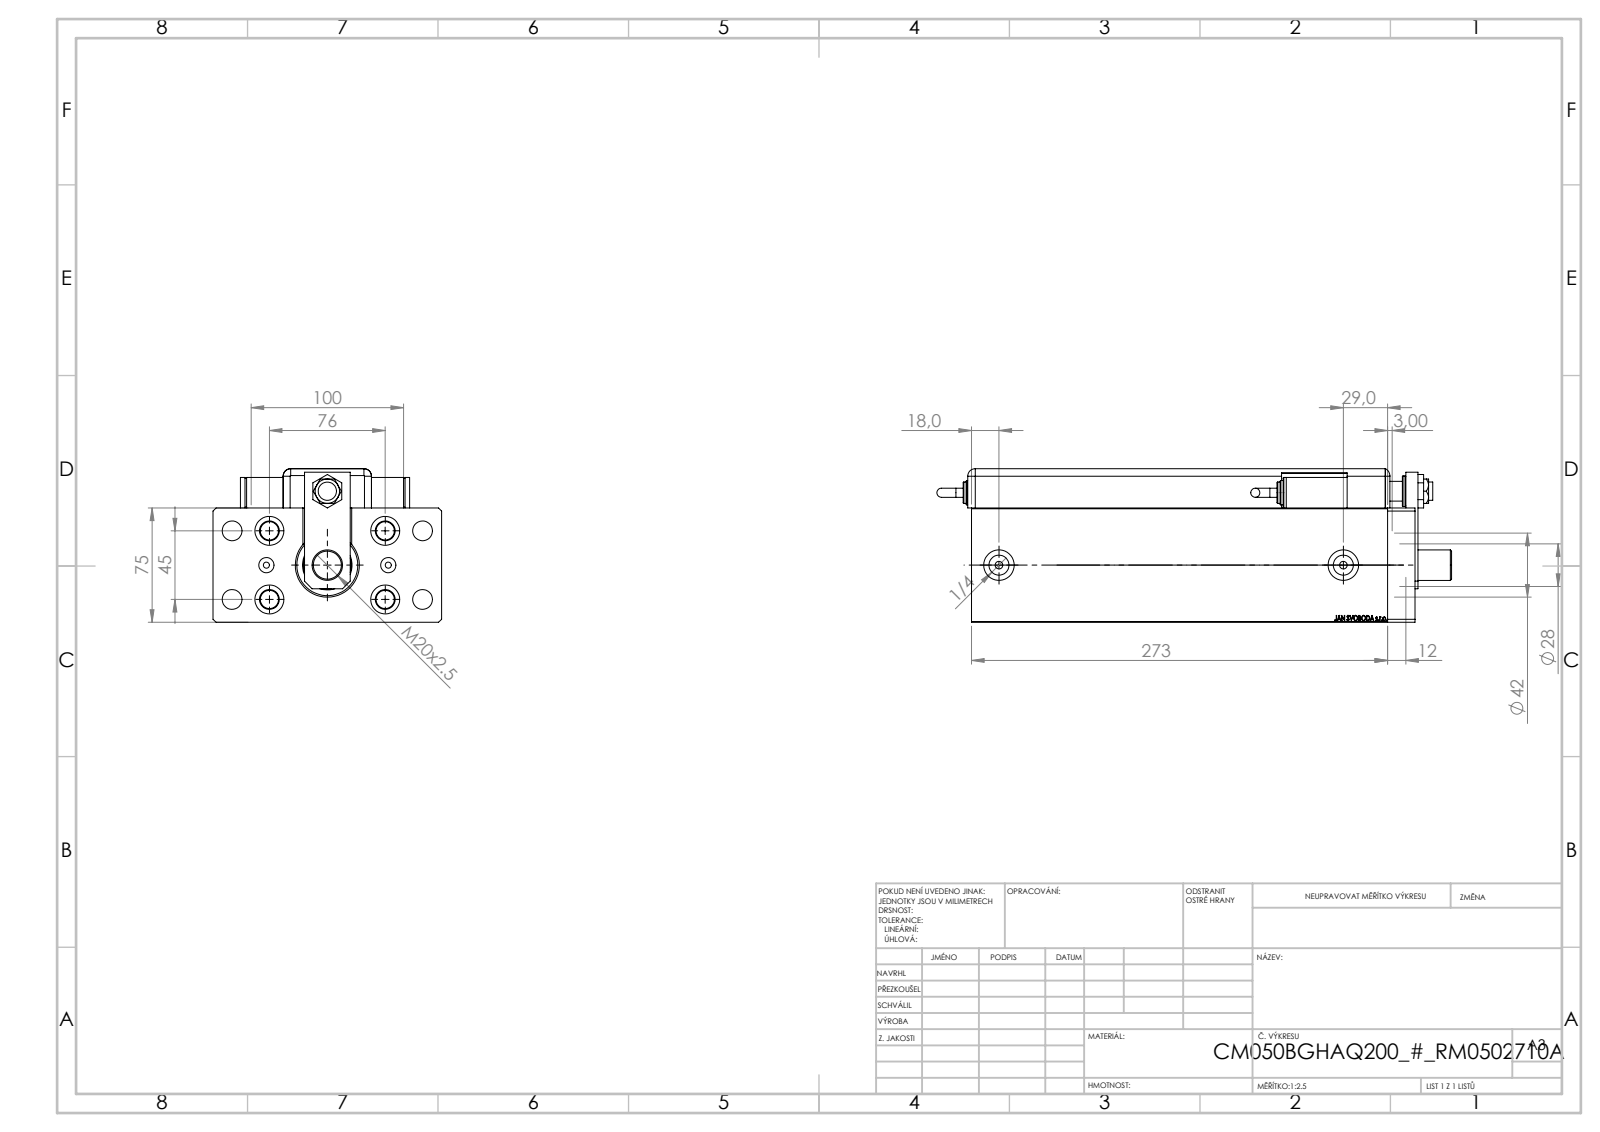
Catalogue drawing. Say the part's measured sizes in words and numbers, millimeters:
The part is named "V450CM_B_Body; MAGNETIC SWITCH Q; V450CM_B_VCP; V450CM_MALE_METRIC (+7 more)". Its 3-D file was written by "SolidWorks 2019 (CONFIG_CONTROL_DESIGN)". It is 15 solids with 1335 faces: 631 planar, 149 cylindrical and 555 other. Overall it measures 337.76 by 150 by 100.8 millimeters. Its volume is 2 134 000 cubic millimeters and its surface area 334 092 square millimeters. Round holes: 9 of diameter 13, 5 of diameter 12, 4 of diameter 4, 4 of diameter 19, 3 of diameter 20, 2 of diameter 5, 2 of diameter 8, 2 of diameter 10, 2 of diameter 13.16, 1 of diameter 14, 1 of diameter 18.5, 1 of diameter 28. Round bosses or shafts: 3 of diameter 20, 2 of diameter 16, 2 of diameter 14, 2 of diameter 6, 1 of diameter 18. Partial cylindrical surfaces (rounded edges, fillets, slot ends): 9 of radius 5, 1 of radius 10, 1 of radius 13.5. The main face-to-face distances are 75, 3, 100, 25.8, 100.8, 21, 97.8, 22.8, 24, 79. The hole center spacings are 22.59, 24.5, 31.82, 44.16, 45, 51.24, 66.43, 81.18.
